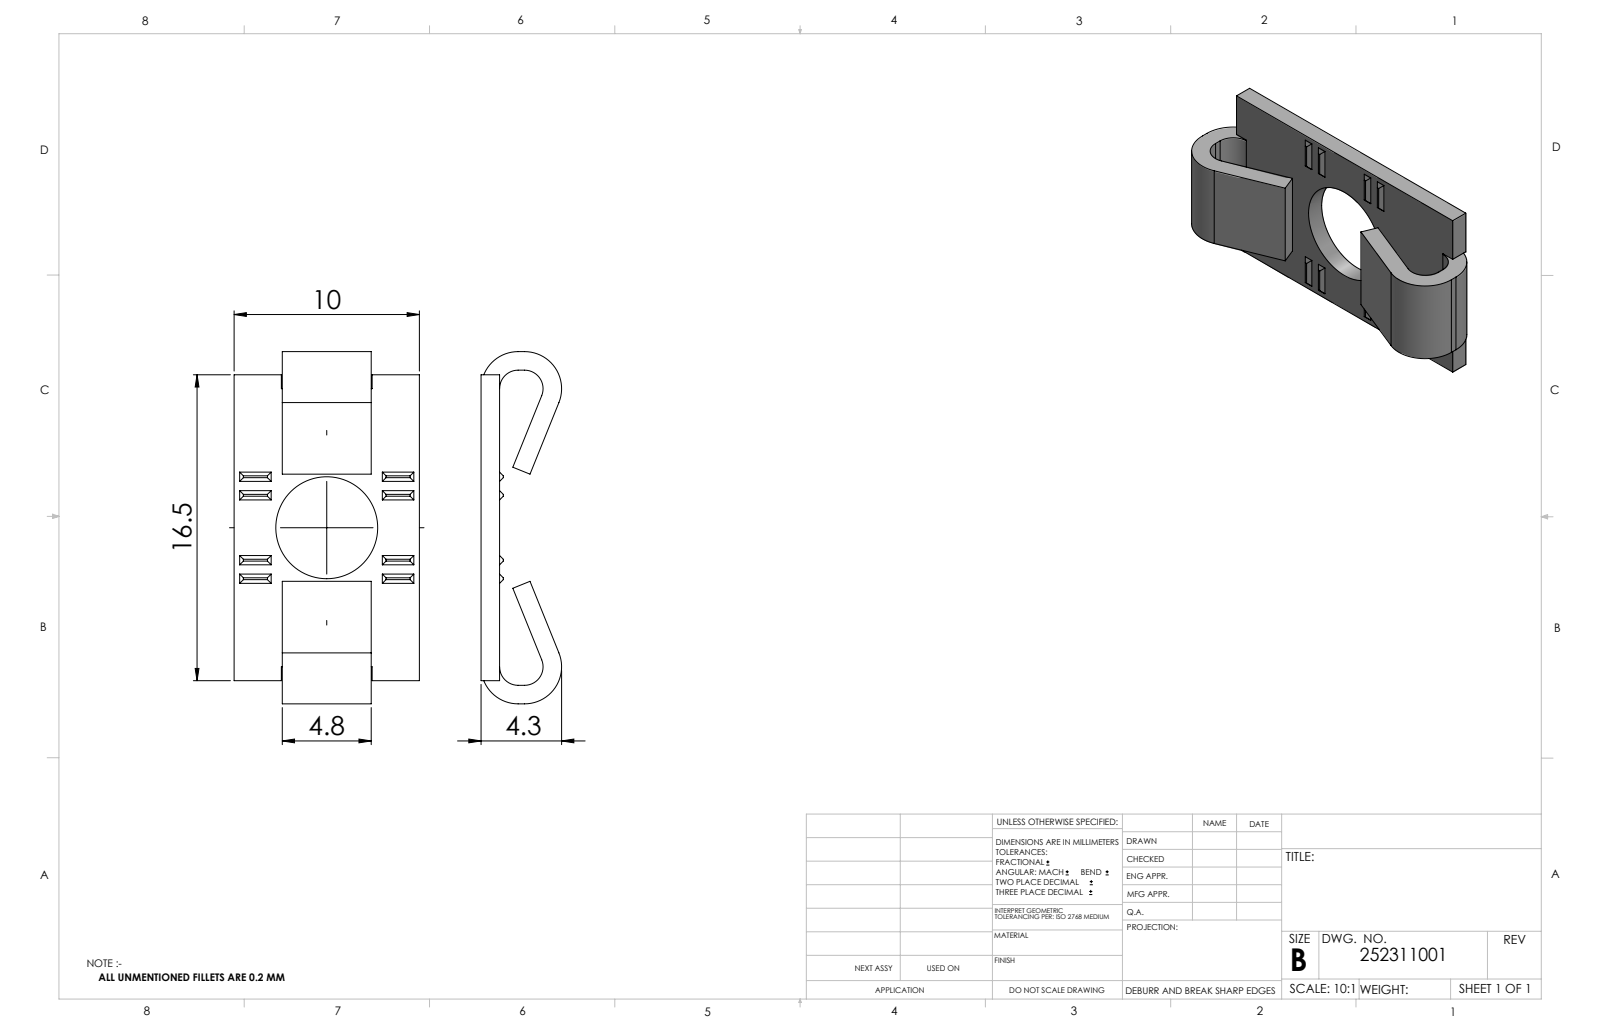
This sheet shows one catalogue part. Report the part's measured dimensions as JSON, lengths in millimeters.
{"part_name": "252311001_c_1", "step_written_by": "SolidWorks 2014 (CONFIG_CONTROL_DESIGN)", "units": "millimeters", "bodies": {"solids": 1, "faces": 82, "planar": 70, "cylindrical": 12, "other": 0}, "overall_size": [19, 10, 4.35], "volume_mm3": 229, "surface_area_mm2": 571, "round_holes": [[5.5, 1]], "partial_cylinders_radius": [[1, 4], [2, 4]], "face_to_face_distances": [1, 2.6, 7.4, 4.8, 10, 16.5, 0.71, 3.18, 1.25, 17.75]}
